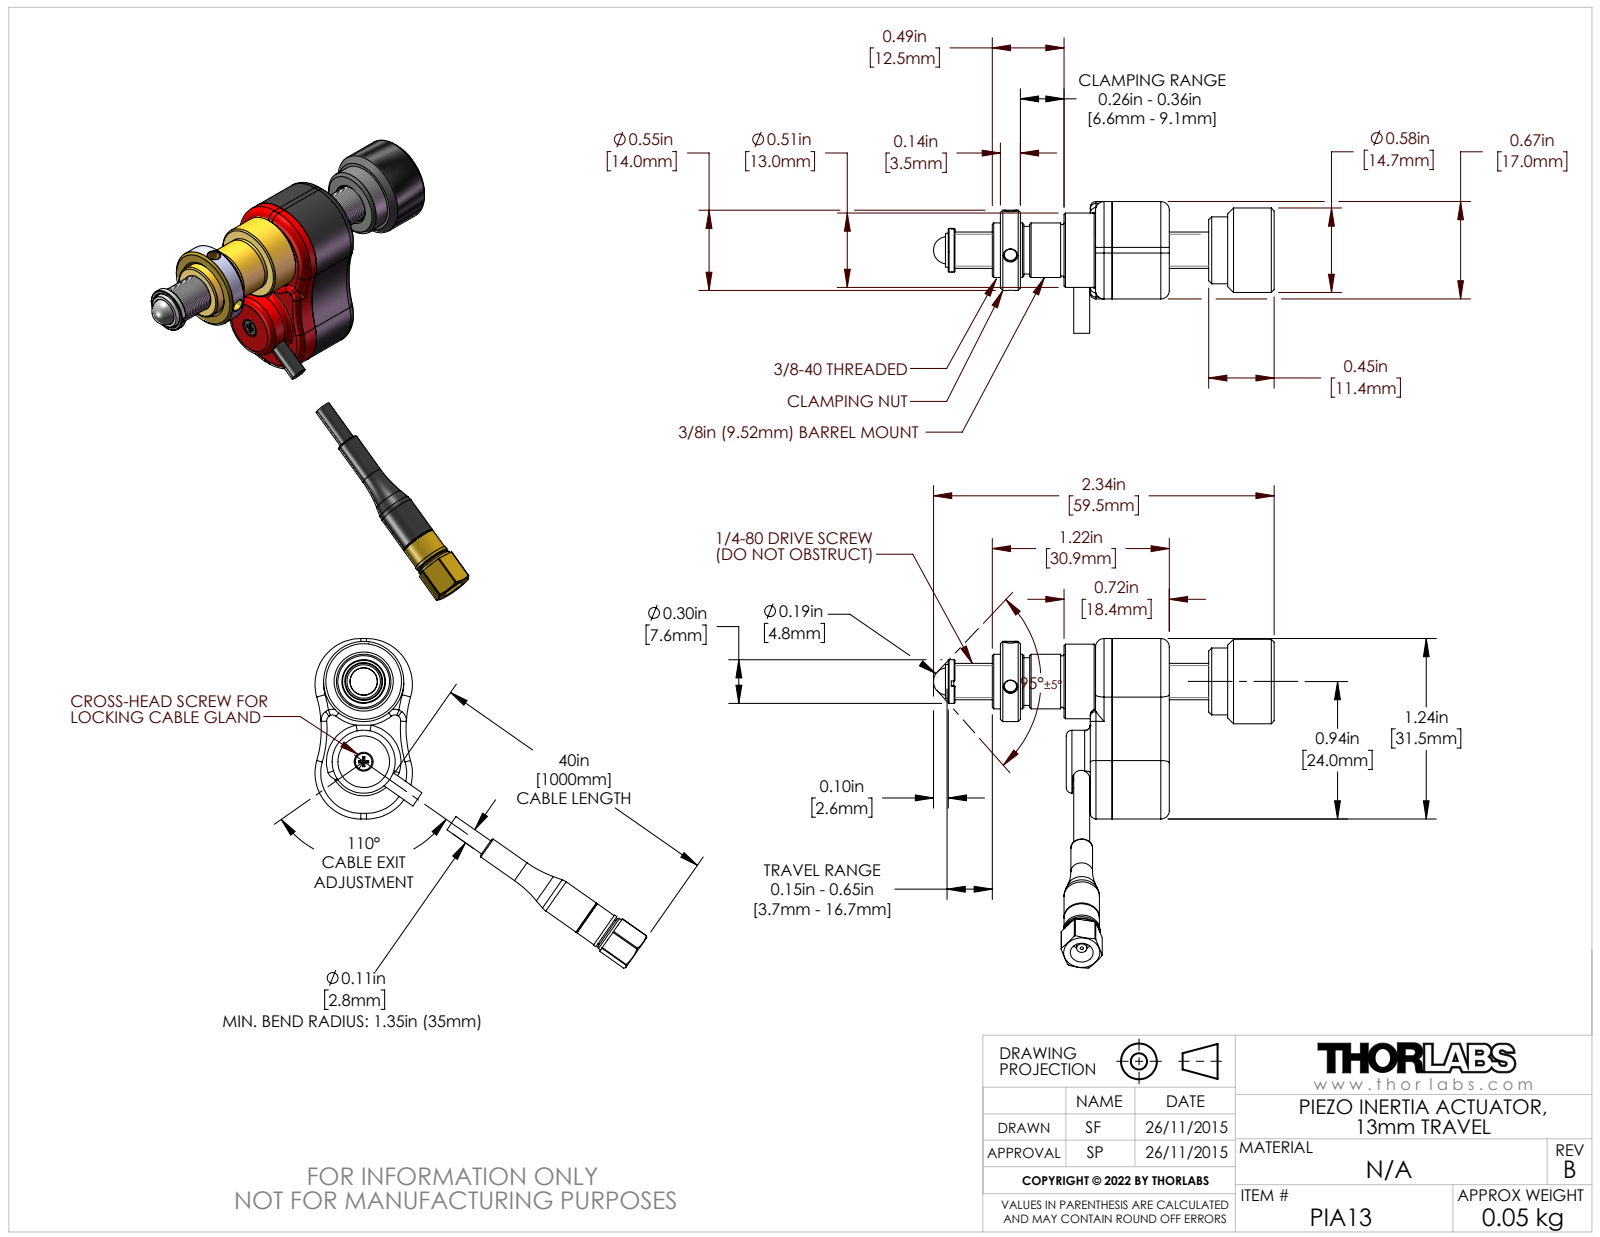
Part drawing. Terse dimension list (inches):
name: Copy of SMC Straight Plug_Crimp_R112075000_Farnell 4194305^169745-SMC Cable-1m; F25SC1-1; CF0204 - 3_16 Tungsten Carbide-Cobalt Ball; 137831-Rod End Boss (+8 more)
written by: SolidWorks 2022 (CONFIG_CONTROL_DESIGN)
unit: in
bodies: 23 solids, 1637 faces (680 planar, 392 cylindrical, 565 other)
size: 2.342 × 2.28 × 2.265
volume: 0.48 in³; area: 17.67 in²
holes: 4× ⌀0.049, 4× ⌀0.087, 3× ⌀0.071, 2× ⌀0.035, 1× ⌀0.019, 1× ⌀0.022, 1× ⌀0.031, 1× ⌀0.063, 1× ⌀0.079, 1× ⌀0.08, 1× ⌀0.11, 1× ⌀0.118
bosses: 6× ⌀0.056, 4× ⌀0.118, 2× ⌀0.063, 1× ⌀0.58, 1× ⌀0.551, 1× ⌀0.512, 1× ⌀0.46, 1× ⌀0.433
rounds: 18× R0.039, 6× R0.059, 6× R0.079, 4× R0.02, 4× R0.069, 4× R0.071, 4× R0.276, 4× R0.283
face distances: 0.358, 0.031, 0.098, 0.303, 0.043, 0.39, 0.028, 0.291, 0.476, 0.508
hole spacings: 0.197, 0.341, 0.748, 0.484, 0.062, 0.183, 0.186, 0.205
